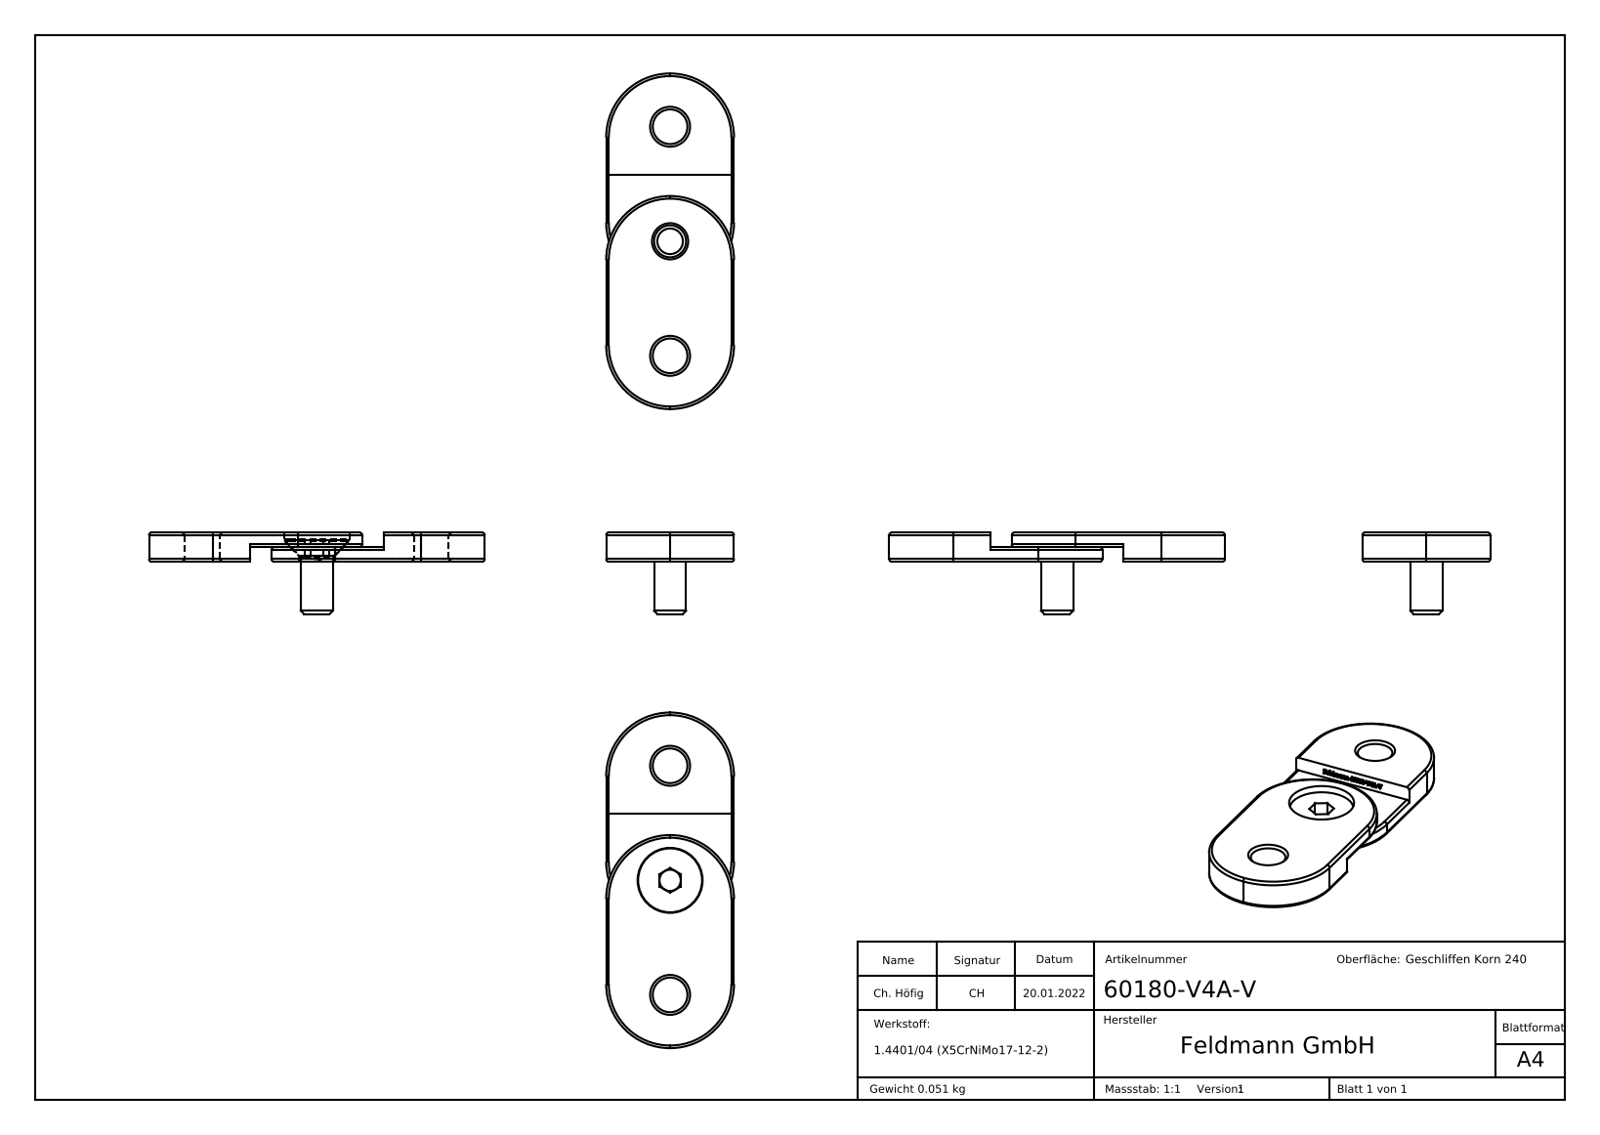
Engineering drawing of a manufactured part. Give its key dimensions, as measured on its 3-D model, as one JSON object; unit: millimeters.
{"part_name": "6018X-240-V Teil2_60180-V4A-V Teil2; 6018X-240-V Teil1; 60180-V4A-V; 6018X-240-V Teil1_60180-V4A-V Teil1 (+3 more)", "step_written_by": "SolidWorks 2018 (CONFIG_CONTROL_DESIGN)", "units": "millimeters", "bodies": {"solids": 3, "faces": 322, "planar": 164, "cylindrical": 32, "other": 126}, "overall_size": [63, 24, 15.3], "volume_mm3": 6429, "surface_area_mm2": 4743, "round_holes": [[6.5, 2], [6.8, 1], [12.2, 1]], "round_bosses_or_shafts": [[12, 1], [6, 1]], "partial_cylinders_radius": [[0.5, 8], [12, 4]], "face_to_face_distances": [2.75, 5.5, 4.2, 1.45, 1.3, 24, 25, 14, 9.8, 12.55], "hole_center_spacings": [21.5, 43]}
